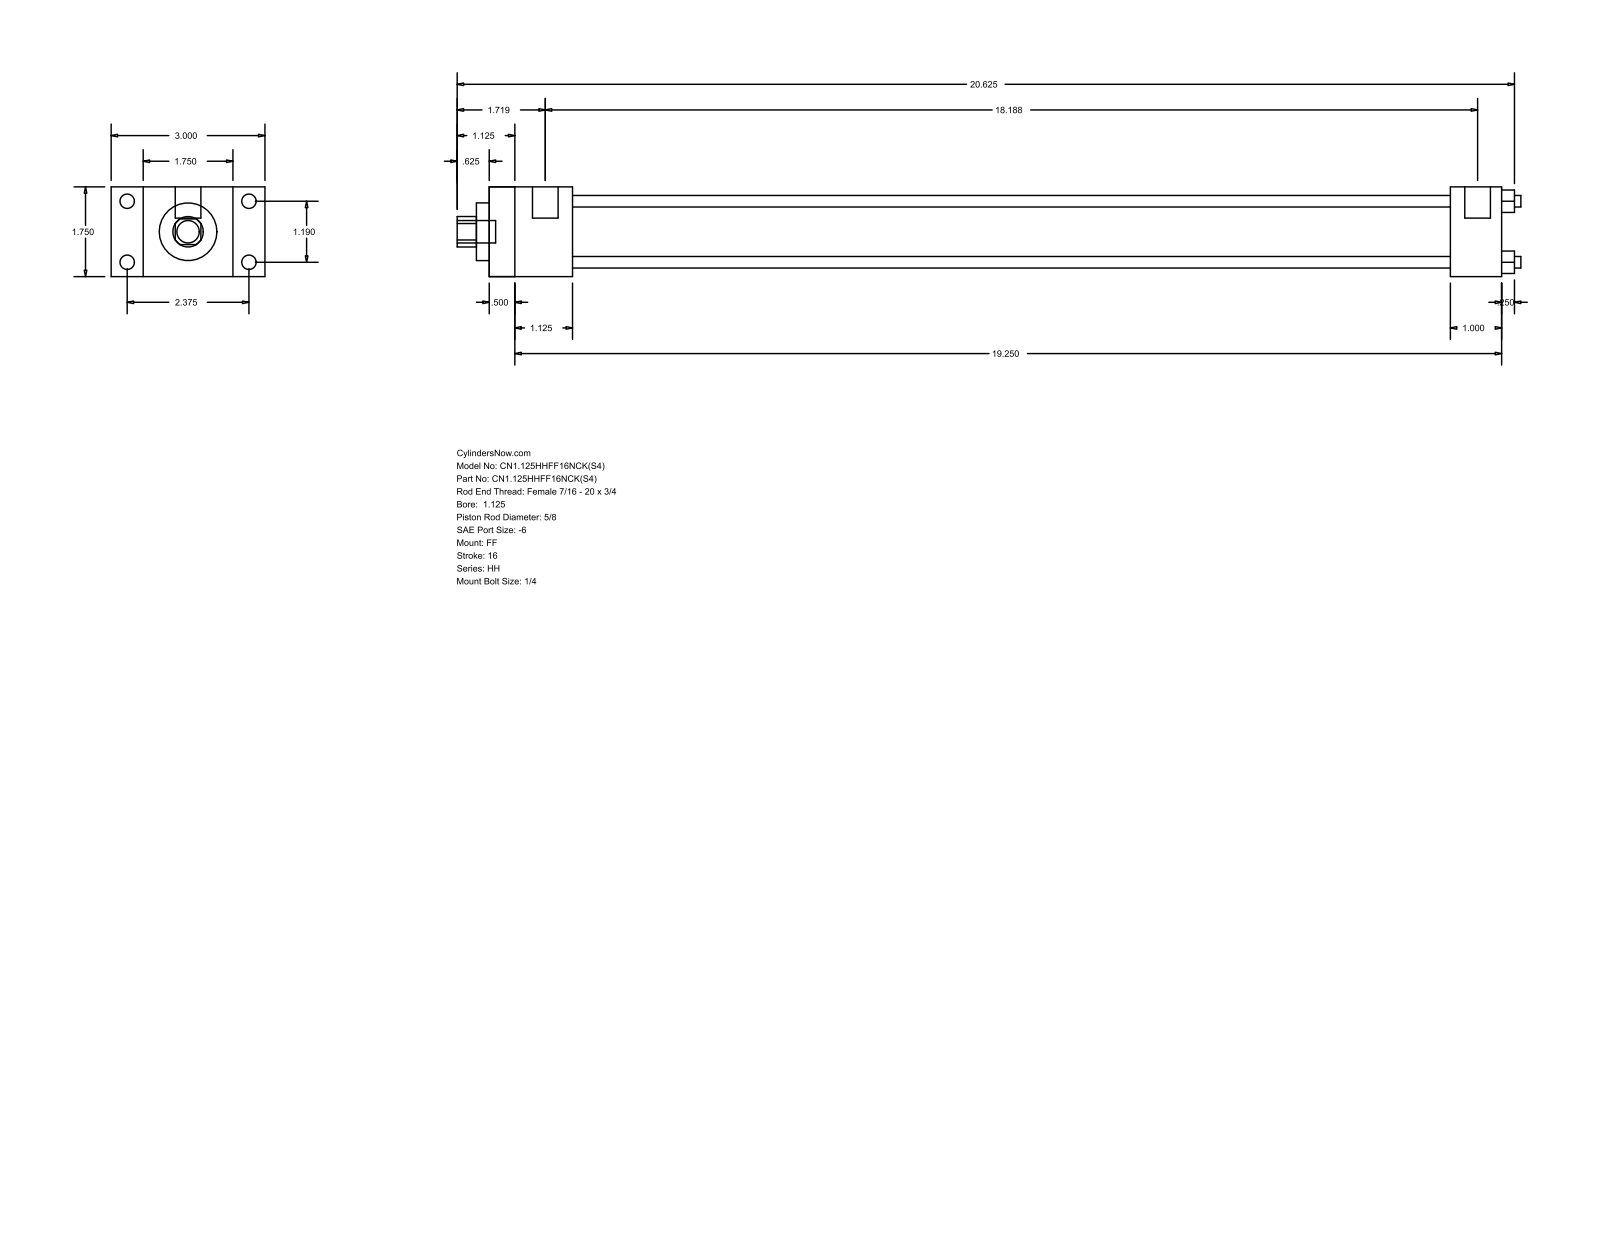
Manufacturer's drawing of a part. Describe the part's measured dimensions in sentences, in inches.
The part is named "HH_FF__0112_0.625". Its 3-D file was written by "GSSL Pune (CONFIG_CONTROL_DESIGN)". It is 0 solids with 92 faces: 64 planar, 28 cylindrical and 0 other. Overall it measures 20.75 by 3 by 1.75 inches. Round holes: 4 of diameter 0.225, 1 of diameter 0.625, 1 of diameter 1.125, 1 of diameter 1.375. Round bosses or shafts: 4 of diameter 0.281, 4 of diameter 0.219, 2 of diameter 0.5, 1 of diameter 0.437. Partial cylindrical surfaces (rounded edges, fillets, slot ends): 1 of radius 0.297. The main face-to-face distances are 1.75, 19.75, 0.625, 0.5, 19.25, 2.375, 1.125, 1.625, 18.75, 18.25. The hole center spacings are 0.841, 1.19, 1.683.
